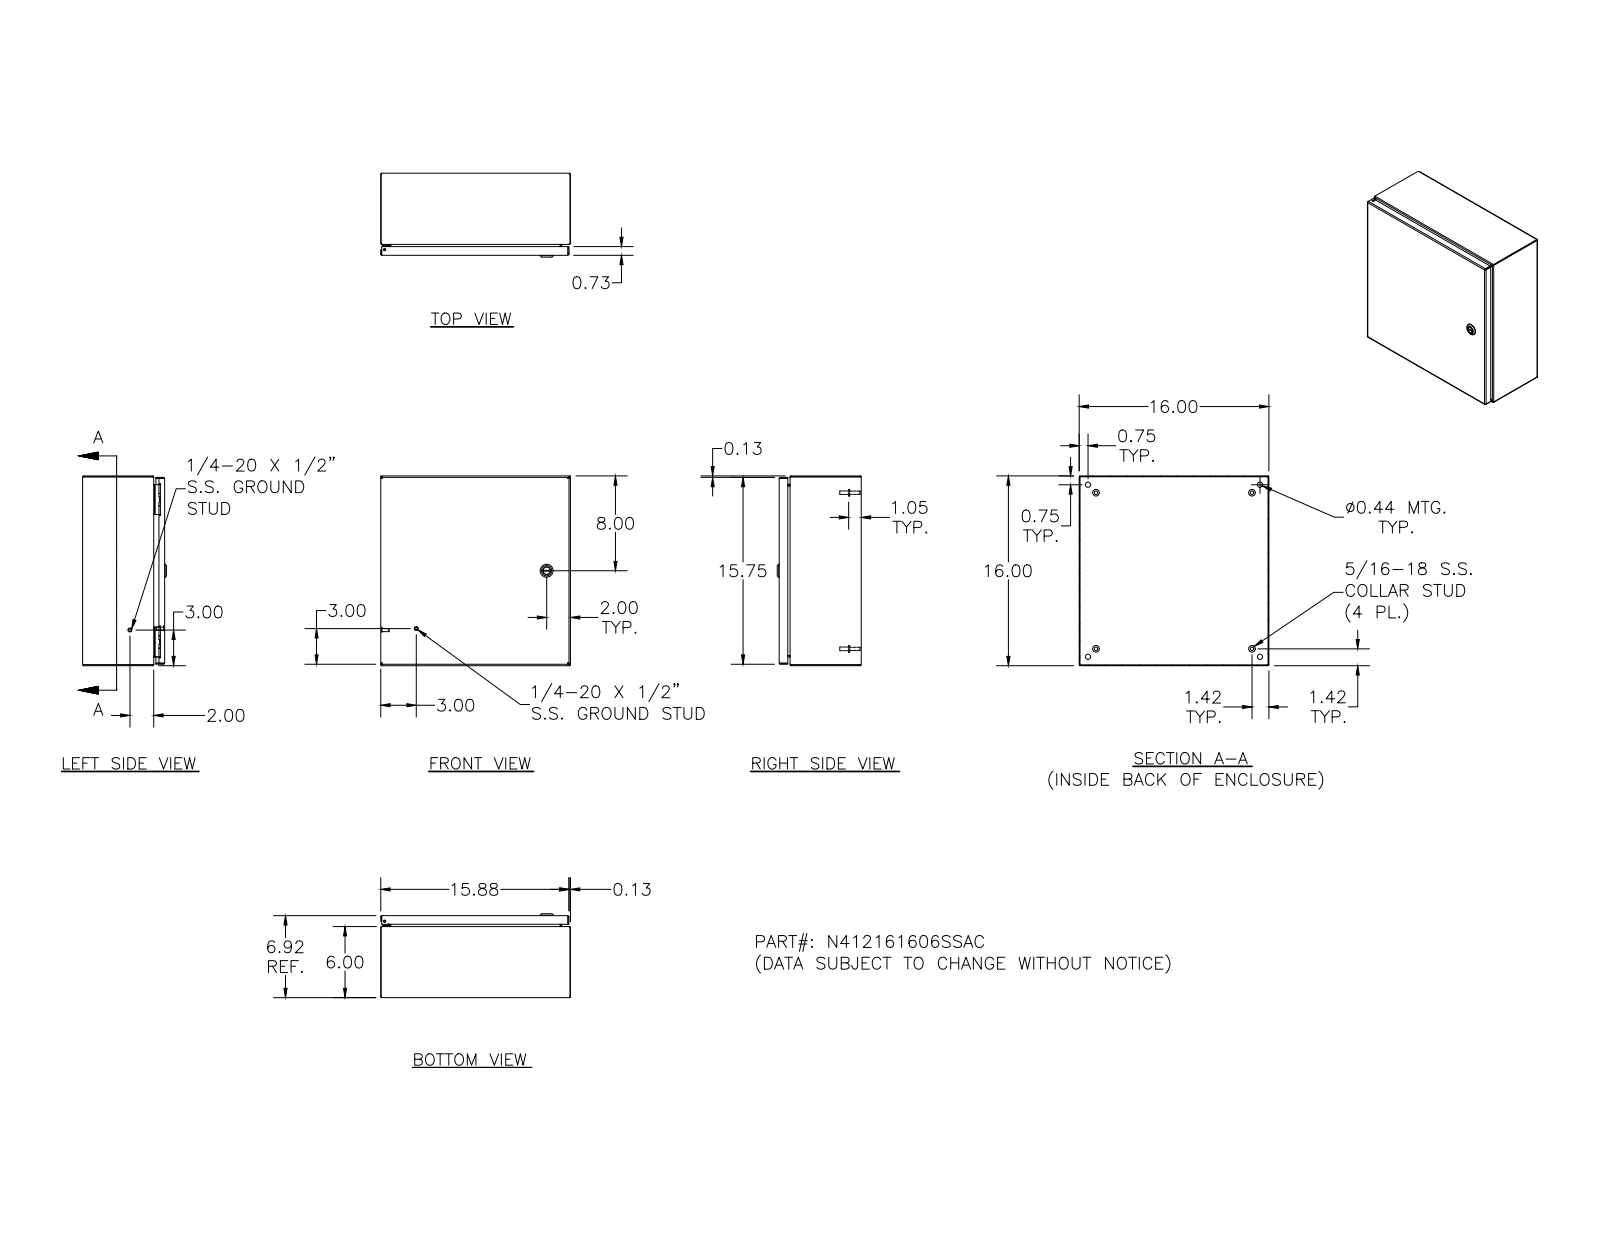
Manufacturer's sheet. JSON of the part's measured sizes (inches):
{"part_name": "N412161606SSAC; N412161606SSACBKP; 388151; N4121616SSACLID (+8 more)", "step_written_by": "Autodesk Inventor 2011 (AUTOMOTIVE_DESIGN)", "units": "inches", "bodies": {"solids": 34, "faces": 1364, "planar": 523, "cylindrical": 497, "other": 344}, "overall_size": [16, 16, 7.075], "volume_in3": 76.42, "surface_area_in2": 2081, "round_holes": [[0.188, 5], [0.093, 4], [0.152, 4], [0.167, 4], [0.172, 4], [0.437, 4], [0.156, 2], [0.187, 1], [0.197, 1], [0.315, 1], [0.394, 1], [0.402, 1]], "round_bosses_or_shafts": [[0.25, 10], [0.563, 4], [0.36, 4], [0.32, 4], [0.3, 4], [0.275, 4], [0.256, 4], [0.164, 4]], "partial_cylinders_radius": [[0.05, 26], [0.016, 18], [0.016, 16], [0.09, 16], [0.031, 14], [0.125, 14], [0.02, 9], [0.032, 8]], "face_to_face_distances": [0.074, 6.843, 15.926, 6.769, 6.917, 15.852, 16, 5.926, 0.917, 0.739], "hole_center_spacings": [12, 0.017, 0.66, 14.5, 0.019, 0.5, 0.648, 0.652]}
